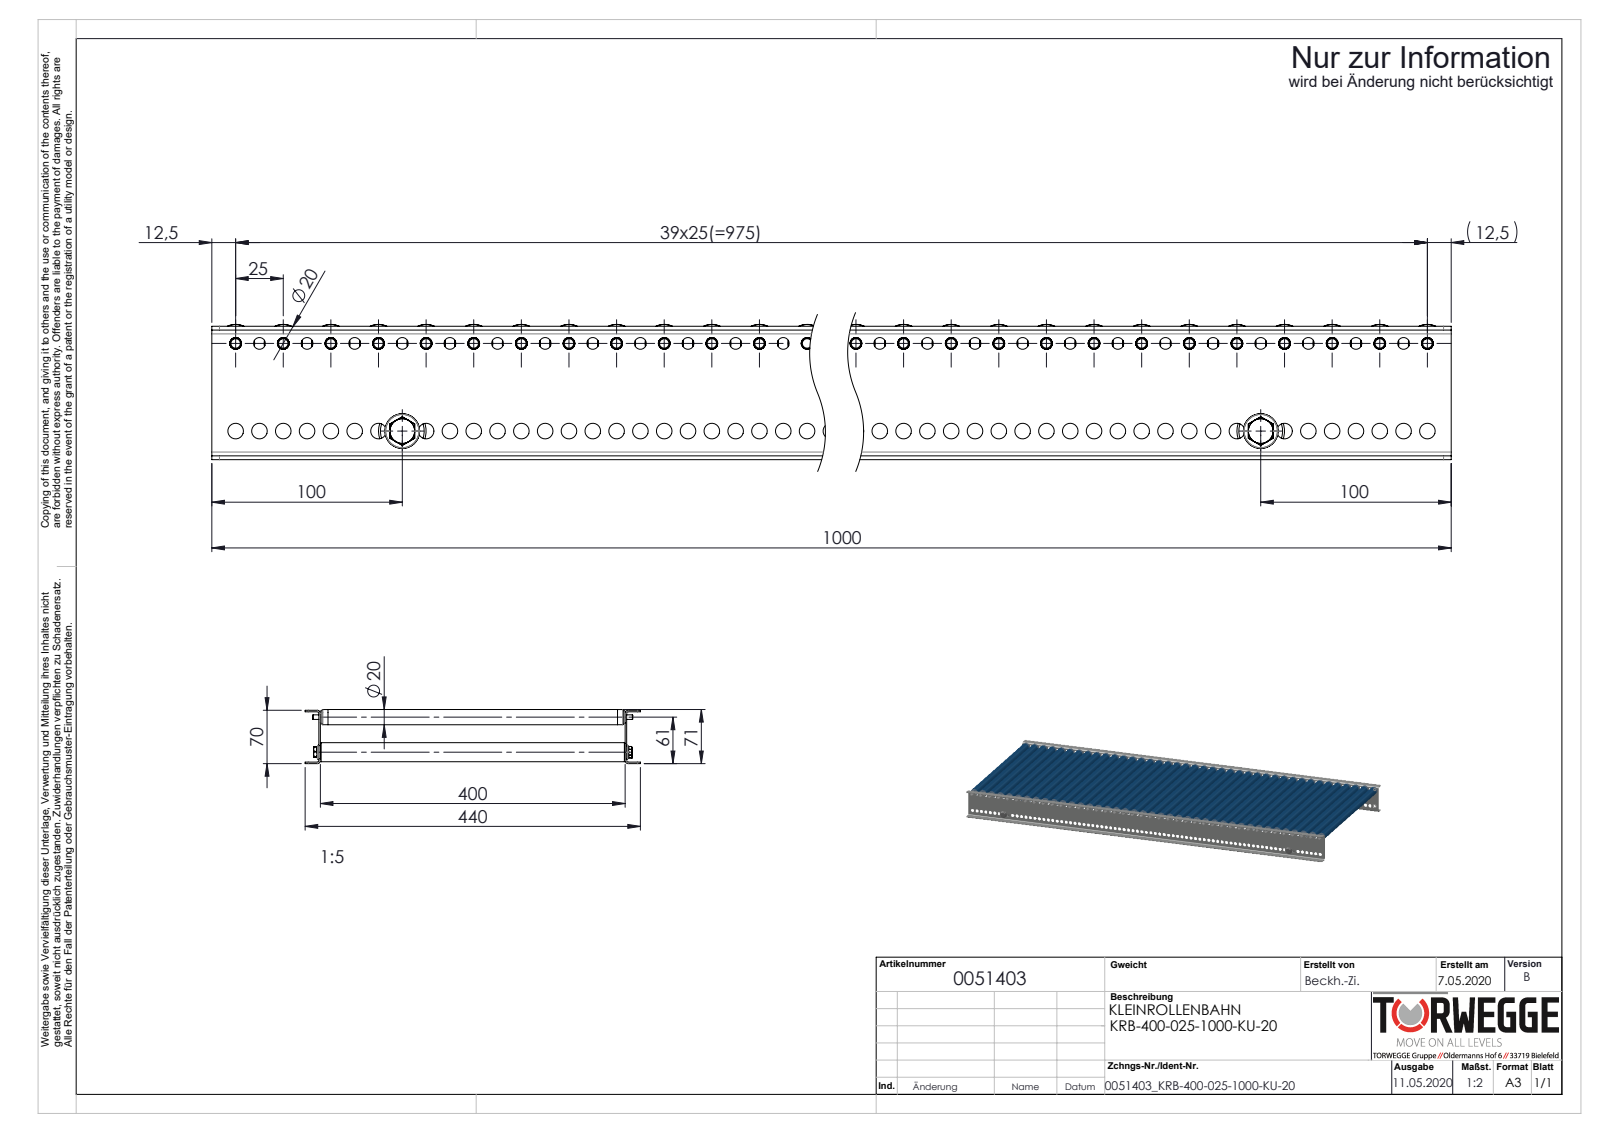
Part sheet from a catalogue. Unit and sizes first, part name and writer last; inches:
Units: inches
Overall size (bounding box): 39.37 × 17.323 × 2.795
Round holes (diameter × count): ⌀0.244 ×79, ⌀0.323 ×79, ⌀0.24 ×40, ⌀0.488 ×40, ⌀0.52 ×40, ⌀0.575 ×40, ⌀0.638 ×40, ⌀0.669 ×40, ⌀0.677 ×40, ⌀0.268 ×2, ⌀0.827 ×2
Round bosses / shafts (diameter × count): ⌀0.787 ×40, ⌀0.783 ×40, ⌀0.673 ×40, ⌀0.661 ×40, ⌀0.65 ×40, ⌀0.449 ×40, ⌀0.437 ×40, ⌀0.402 ×40
Partial cylindrical surfaces — rounded edges, fillets, slot ends (radius × count): R0.159 ×40, R0.157 ×8, R0.079 ×4
Main face-to-face distances: 0.079, 15.827, 2.677, 15.748, 15.906, 2.598, 2.756, 15.433, 0.394, 0.472
Hole centre spacings: 0.492, 0.984, 1.476, 1.969, 2.461, 2.953, 3.445, 3.937
Volume: 159 in³ · Surface area: 4 608 in²
Bodies: 252 solids, 10672 faces (3560 planar, 3968 cylindrical, 3144 other)
Part name (STEP PRODUCT): 0017012_Tragrollenrohr-Ø20x1,5KU_KFG_L380; S100994_Sperrzahnschraube_M08x16-8.8-A2K; Traversen_KFG_L400; 0051403 (+4 more)
STEP written by: SolidWorks 2020 (AUTOMOTIVE_DESIGN)
